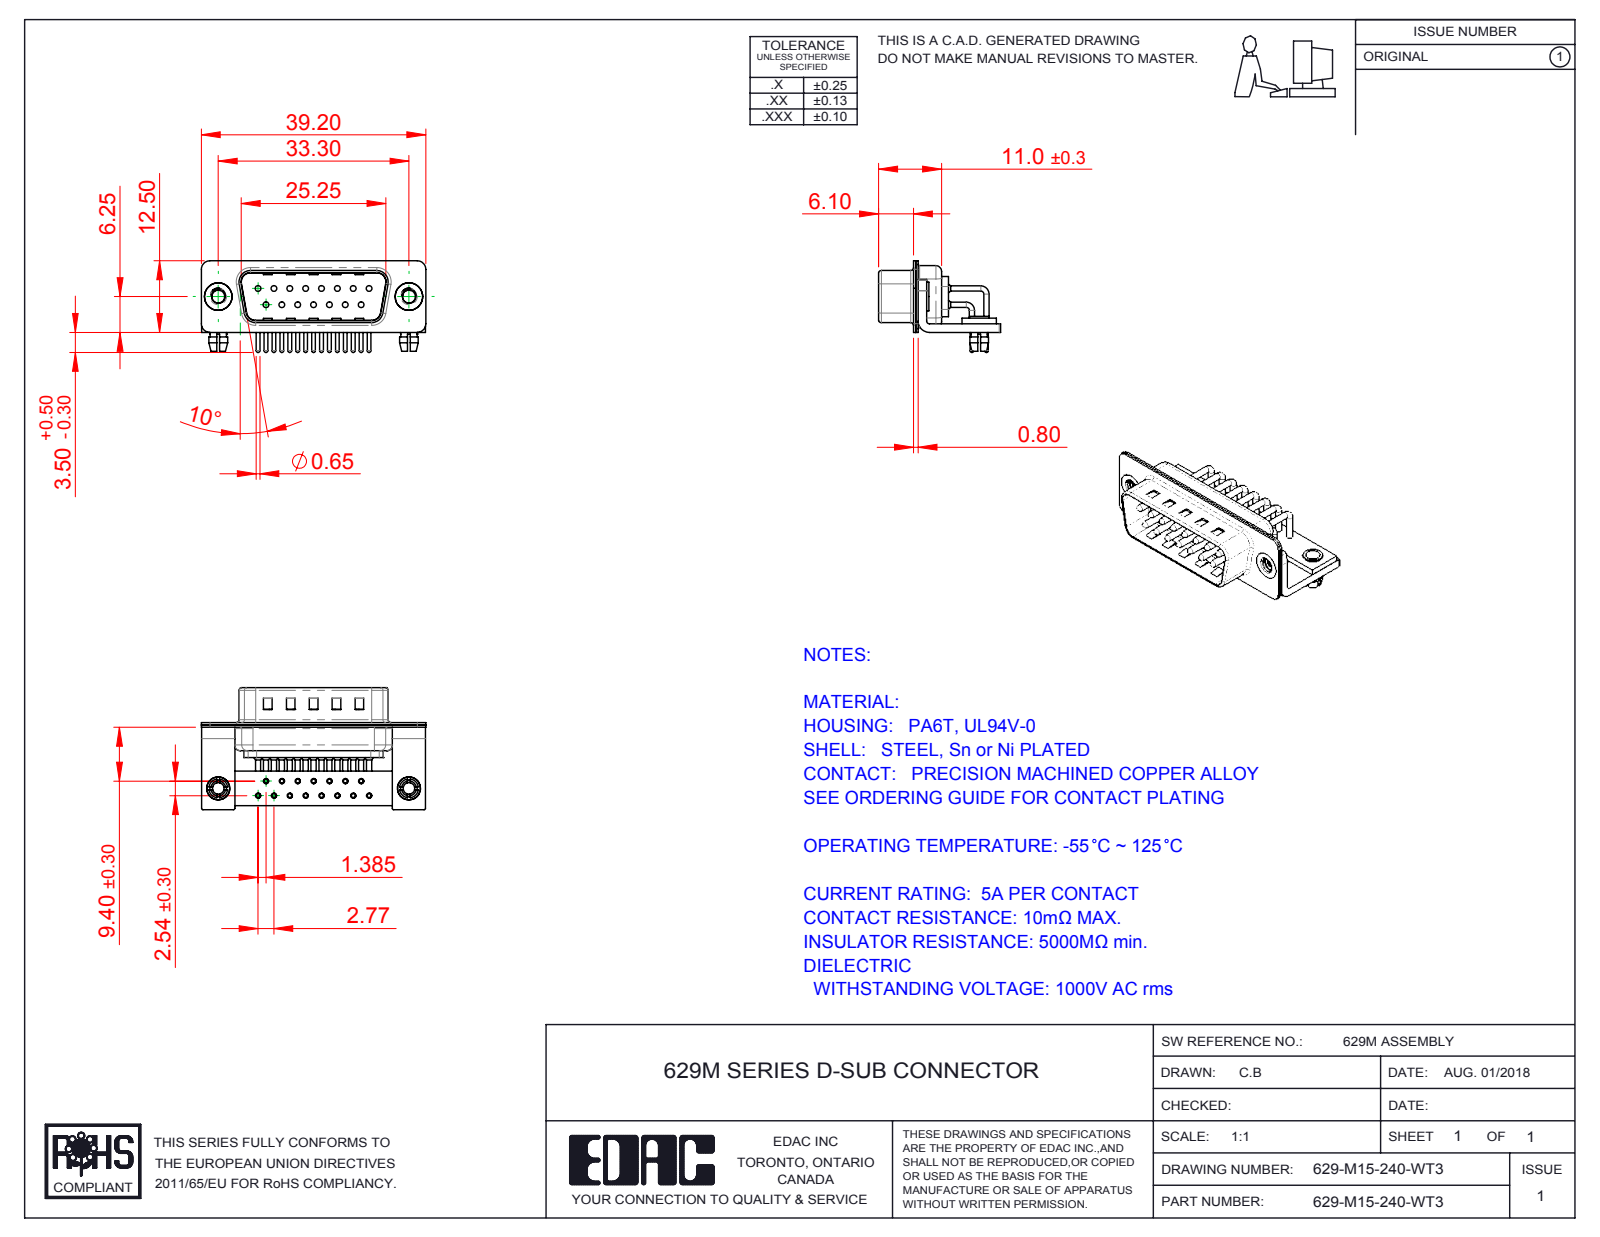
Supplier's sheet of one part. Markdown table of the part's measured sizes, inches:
| quantity | value |
| --- | --- |
| part name | 629M Board Lock; 629M Stabilizer Bracket; 629M 4-40 Threaded Rivet_Stabilizer; 629M Shell Rear_15 Contacts (+6 more) |
| STEP written by | SolidWorks 2016 (CONFIG_CONTROL_DESIGN) |
| units | inches |
| bodies | 25 solids, 2162 faces (1173 planar, 757 cylindrical, 232 other) |
| overall size | 1.543 × 0.839 × 0.63 |
| volume | 0.151 in³ |
| surface area | 10.48 in² |
| round holes (diameter × count) | 0.079 × 17, 0.035 × 15, 0.039 × 15, 0.067 × 15, 0.089 × 2, 0.098 × 2, 0.126 × 2, 0.157 × 2, 0.189 × 2 |
| round bosses / shafts (diameter × count) | 0.035 × 21, 0.059 × 15, 0.026 × 15, 0.197 × 2, 0.193 × 2, 0.157 × 2, 0.134 × 2, 0.13 × 2 |
| partial cylindrical surfaces (radius × count) | 0.01 × 16, 0.059 × 16, 0.04 × 15, 0.079 × 13, 0.02 × 9, 0.063 × 8, 0.024 × 4, 0.026 × 4 |
| main face-to-face distances | 0.016, 0.059, 0.033, 0.031, 0.049, 0.409, 0.376, 0.039, 0.075, 0.36 |
| hole center spacings | 0.109, 0.218, 0.124, 0.327, 0.192, 0.436, 0.114, 0.29 |
